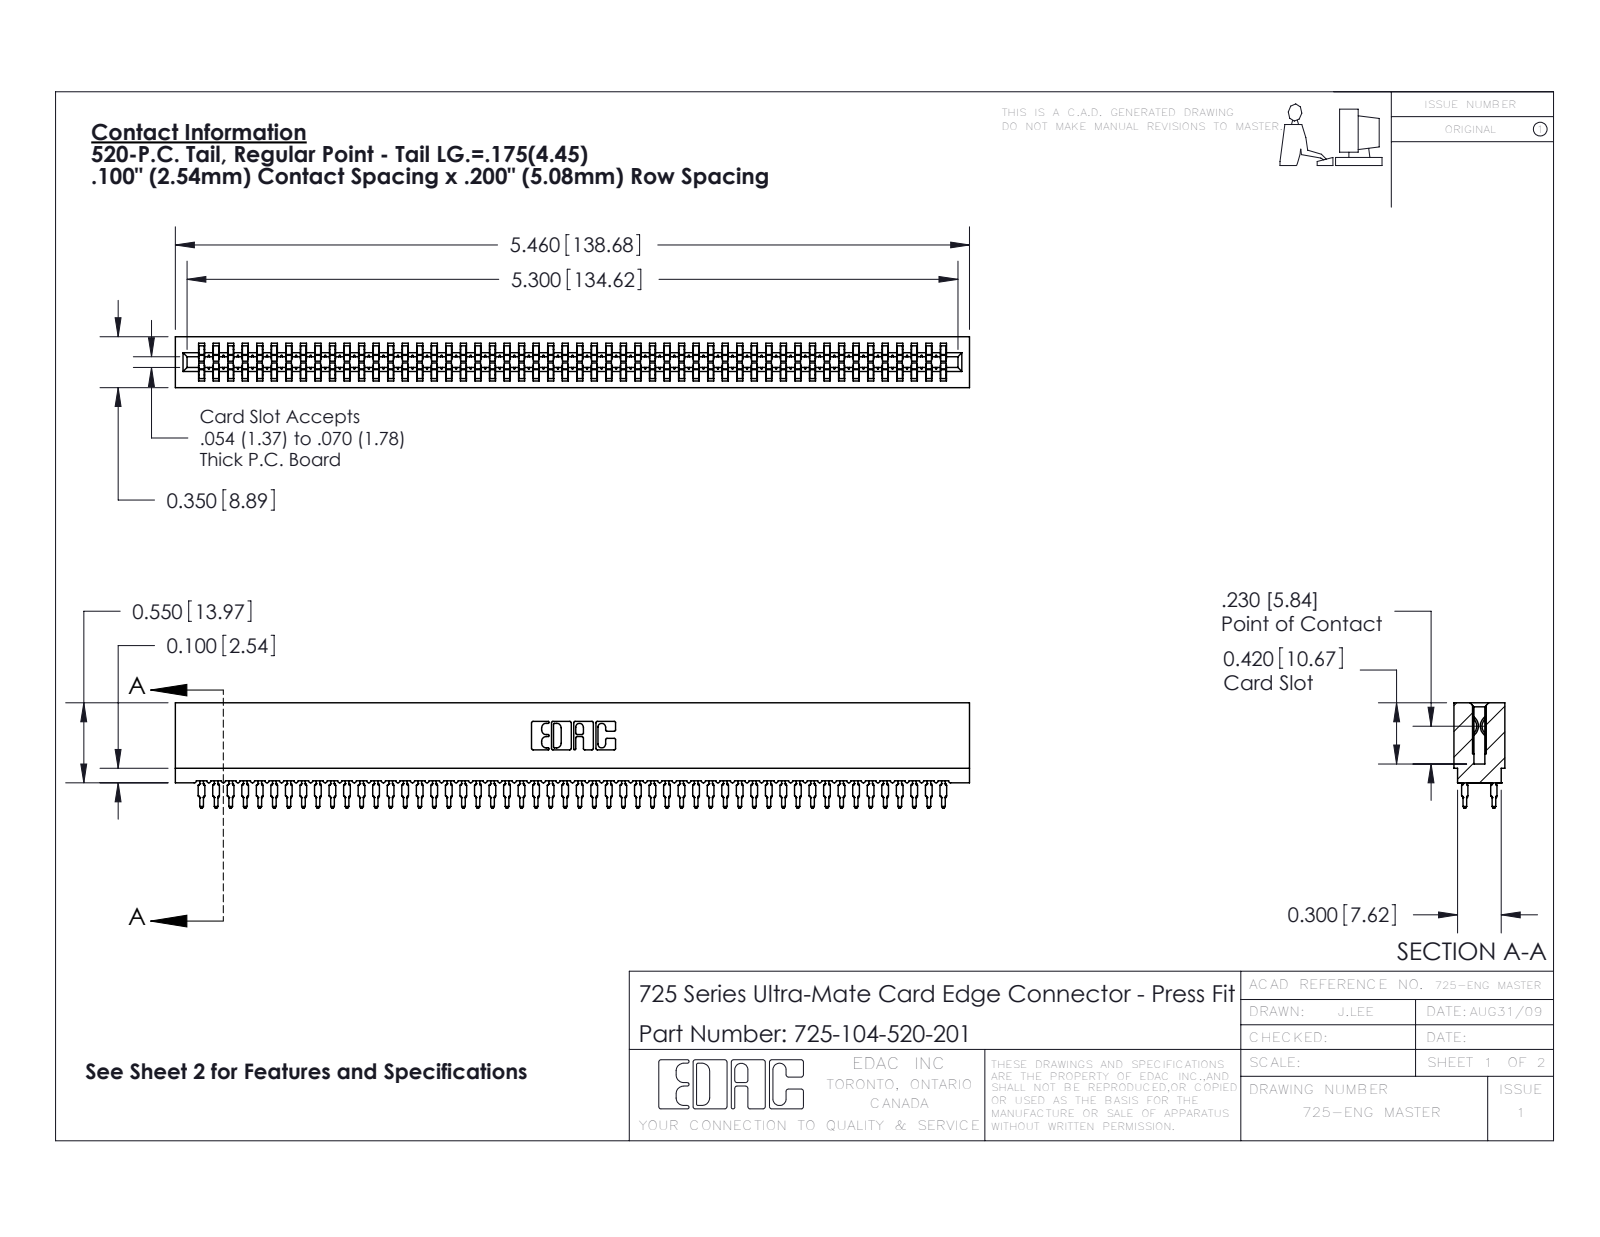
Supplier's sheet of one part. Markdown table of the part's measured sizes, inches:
| quantity | value |
| --- | --- |
| part name | 725 Part_Insulator Option - 01; 745-292-001_520; 725-104-520-201 |
| STEP written by | SolidWorks 2016 (CONFIG_CONTROL_DESIGN) |
| units | inches |
| bodies | 105 solids, 9403 faces (4839 planar, 1860 cylindrical, 2704 other) |
| overall size | 5.46 × 0.725 × 0.35 |
| volume | 0.662 in³ |
| surface area | 35.04 in² |
| partial cylindrical surfaces (radius × count) | 0.021 × 208, 0.015 × 104, 0.01 × 22, 0.005 × 8, 0.011 × 8, 0.007 × 6, 0.031 × 6, 0.026 × 3 |
| main face-to-face distances | 0.2, 0.35, 0.063, 0.287, 0.212, 0.138, 0.076, 0.149, 0.305, 0.045 |
